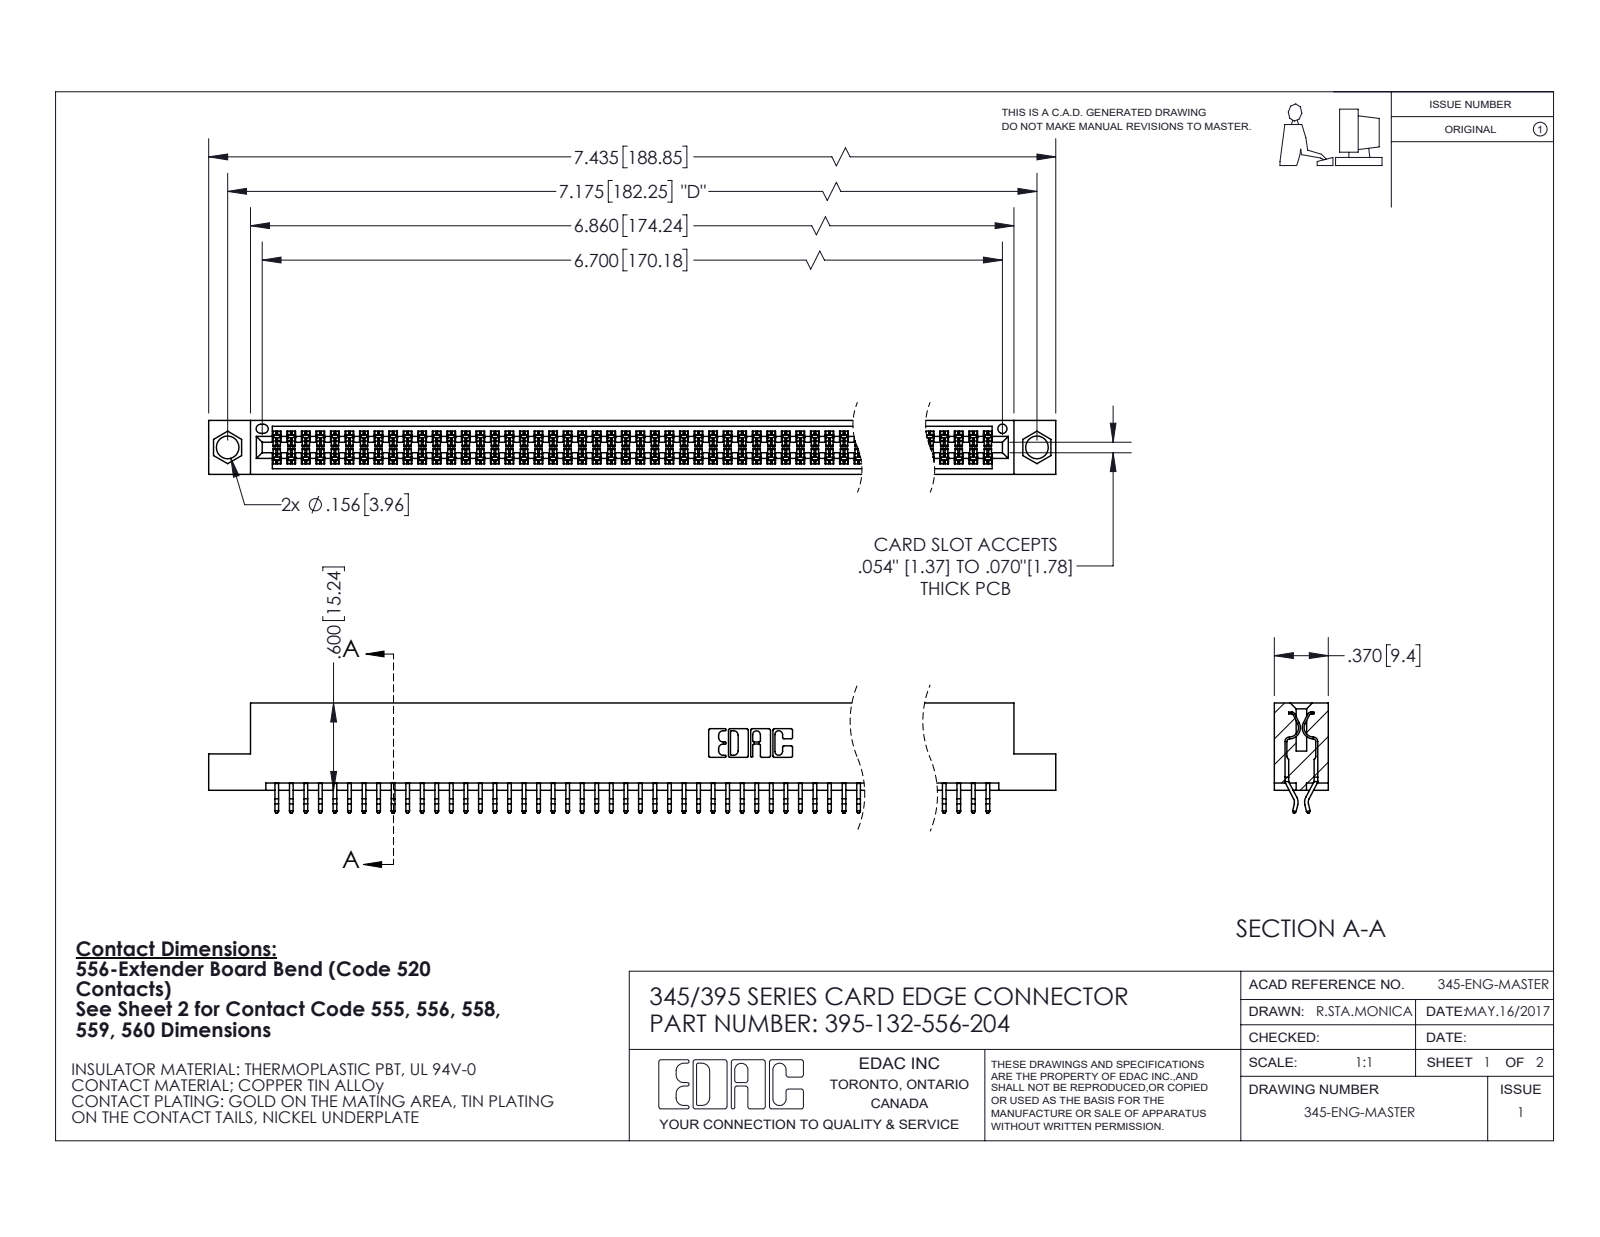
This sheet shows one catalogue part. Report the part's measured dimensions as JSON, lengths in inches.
{"part_name": "395-132-556-204; 345-292-001_556 Tail; 345 Part_Flush Mounting Lugs - 0.156 Dia-TI", "step_written_by": "SolidWorks 2020 (CONFIG_CONTROL_DESIGN)", "units": "inches", "bodies": {"solids": 133, "faces": 7532, "planar": 4978, "cylindrical": 2554, "other": 0}, "overall_size": [7.435, 0.757, 0.37], "volume_in3": 1.126, "surface_area_in2": 42.6, "round_holes": [[0.156, 2], [0.064, 1]], "partial_cylinders_radius": [[0.006, 264], [0.01, 22], [0.007, 6], [0.031, 6], [0.026, 3], [0.01, 2], [0.014, 2], [0.019, 2]], "face_to_face_distances": [0.298, 0.072, 0.37, 0.2, 0.025, 0.098, 0.272, 0.225, 0.175, 0.149], "hole_center_spacings": [0.27, 6.939, 7.175]}
